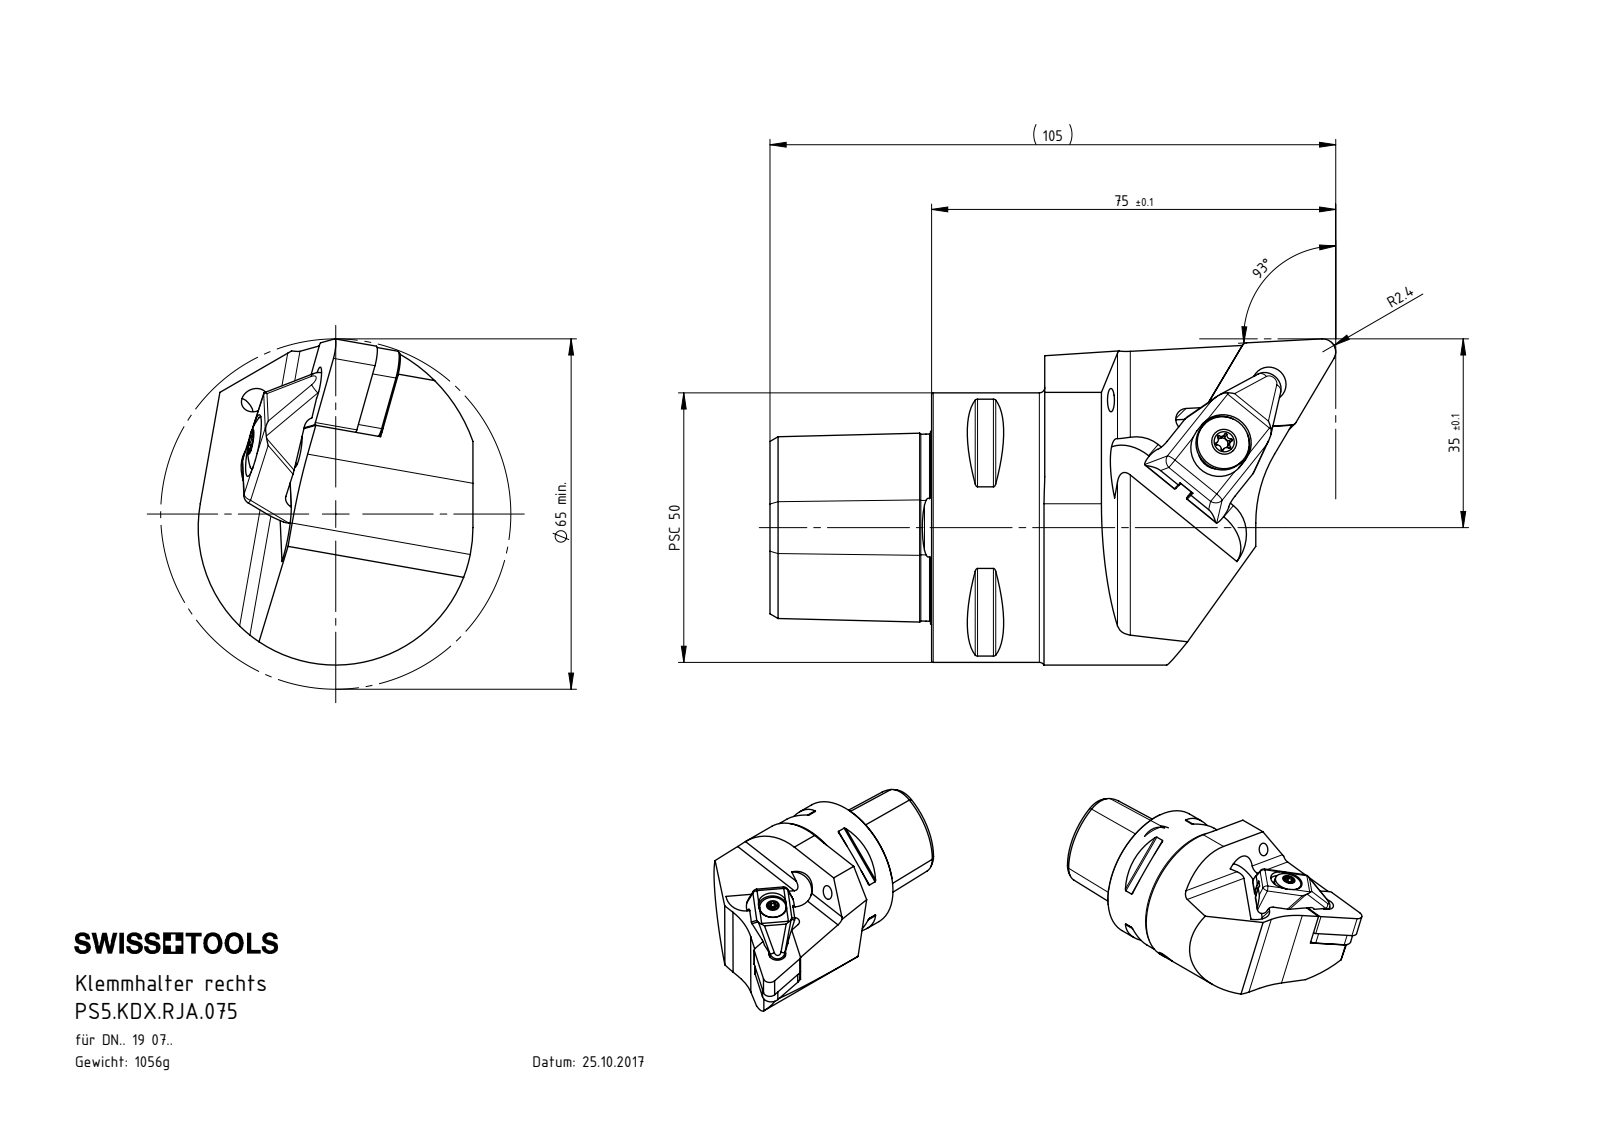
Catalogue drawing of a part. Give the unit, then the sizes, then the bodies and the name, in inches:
Units: inches
Overall size (bounding box): 4.137 × 2.385 × 2.008
Round holes (diameter × count): ⌀0.197 ×3, ⌀0.165 ×2, ⌀0.157 ×1, ⌀0.226 ×1, ⌀0.236 ×1, ⌀0.24 ×1, ⌀0.25 ×1, ⌀0.321 ×1, ⌀0.335 ×1, ⌀0.366 ×1, ⌀0.571 ×1, ⌀0.827 ×1
Round bosses / shafts (diameter × count): ⌀0.236 ×2, ⌀0.197 ×2, ⌀1.969 ×1, ⌀0.386 ×1, ⌀0.276 ×1, ⌀0.256 ×1, ⌀0.228 ×1
Partial cylindrical surfaces — rounded edges, fillets, slot ends (radius × count): R0.008 ×11, R0.063 ×10, R0.02 ×8, R0.015 ×6, R0.028 ×6, R0.13 ×4, R0.027 ×3, R0.027 ×3
Main face-to-face distances: 0.49, 0.609, 0.609, 0.489, 0.189, 0.301, 0.609, 1.181, 2.008, 0.827
Hole centre spacings: 0.016, 0.626, 0.631, 0.634, 0.642, 0.646, 0.649, 1.024
Volume: 8.153 in³ · Surface area: 44.98 in²
Bodies: 10 solids, 419 faces (114 planar, 145 cylindrical, 160 other)
Part name (STEP PRODUCT): Spannschraube; WCC-ER2.001.010_A; PS5-KDX.RJA.075; Bratze (+6 more)
STEP written by: SolidWorks 2017 (CONFIG_CONTROL_DESIGN)
